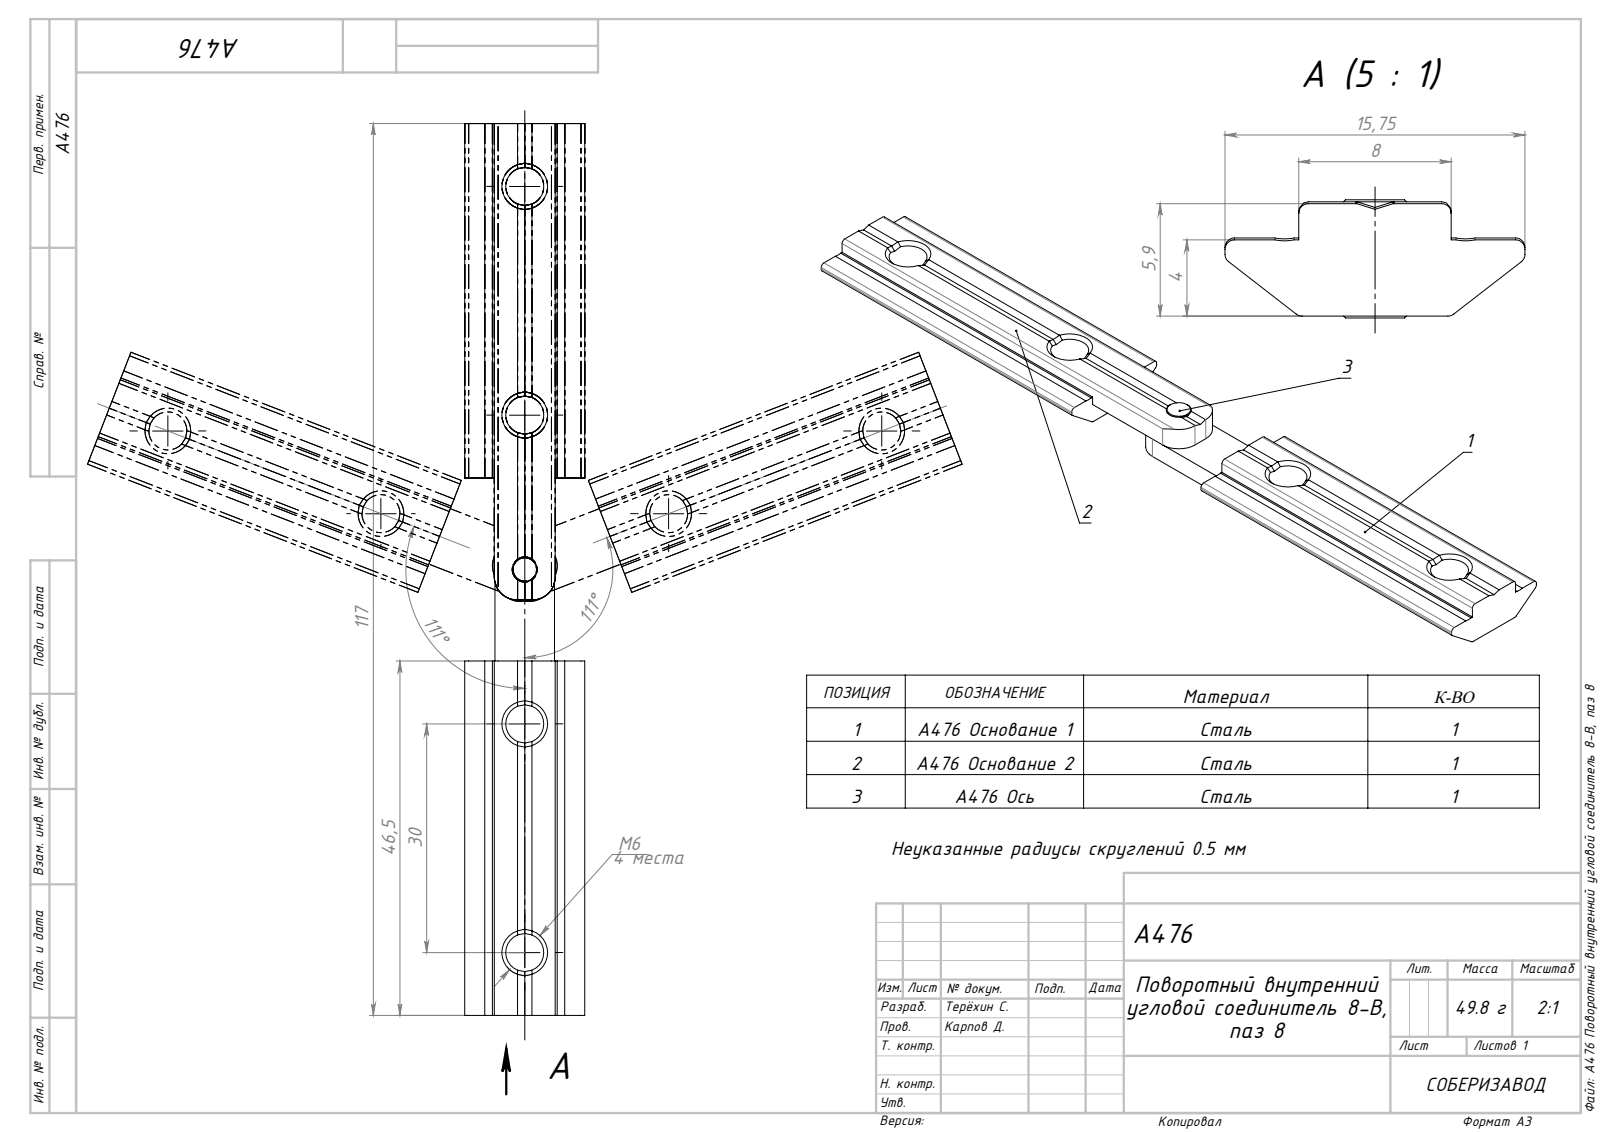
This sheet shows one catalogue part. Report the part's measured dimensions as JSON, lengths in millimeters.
{"part_name": "A476 Основание 1_00; A476 Ось_00; A476 Основание 2_00; A476 Поворотный внутренний угловой соединитель 8-B, паз 8", "step_written_by": "SolidWorks 2021 (AUTOMOTIVE_DESIGN)", "units": "millimeters", "bodies": {"solids": 3, "faces": 132, "planar": 54, "cylindrical": 38, "other": 40}, "overall_size": [117, 15.75, 6.2], "volume_mm3": 6382, "surface_area_mm2": 4783, "round_holes": [[5, 4], [3, 1]], "partial_cylinders_radius": [[0.5, 16], [2.52, 4], [3, 4]], "face_to_face_distances": [5.9, 4, 1.9, 6, 2.8, 1.2, 3.1, 4.1, 2, 3.9], "hole_center_spacings": [20.25, 30, 50.25, 70.5, 40.5, 100.5]}
